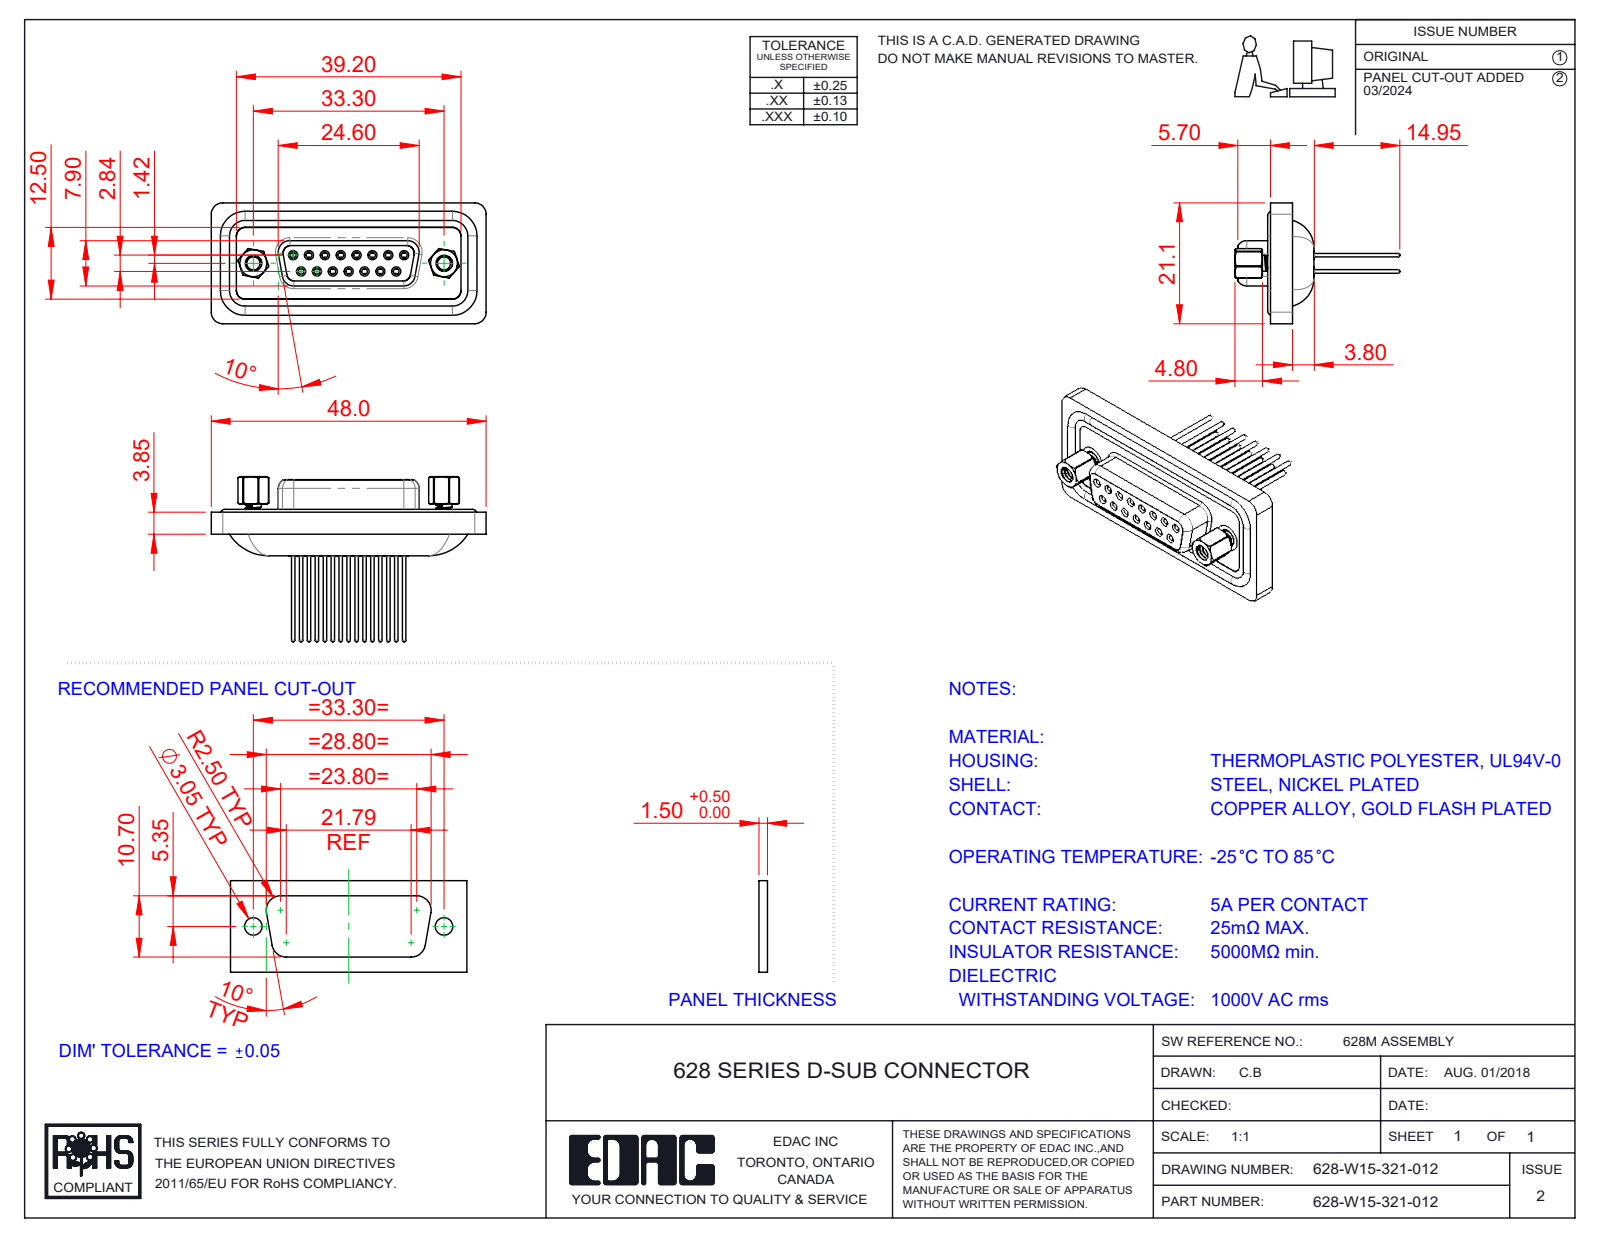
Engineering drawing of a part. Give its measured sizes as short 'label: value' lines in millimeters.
name: 628W Housing_15 Contacts; 628W Shell Front_15 Contacts; 628W 4-40 Threaded Rivet; 628-W15-321-012 (+4 more)
written by: SolidWorks 2020 (CONFIG_CONTROL_DESIGN)
unit: mm
bodies: 23 solids, 1278 faces (326 planar, 535 cylindrical, 417 other)
size: 48 × 28.3 × 21.1
volume: 6 416 mm³; area: 9 985 mm²
holes: 15× ⌀1, 15× ⌀1.1, 15× ⌀1.5, 15× ⌀1.7, 15× ⌀1.8, 15× ⌀2, 2× ⌀2.26, 2× ⌀2.29, 2× ⌀4, 2× ⌀4.8, 2× ⌀5
bosses: 19× ⌀1.6, 15× ⌀2.2, 15× ⌀0.6, 7× ⌀1.5, 2× ⌀4.9, 2× ⌀2.79
rounds: 16× R2, 14× R1.5, 8× R1.35, 6× R2.7, 4× R0.5, 4× R0.9, 4× R1.6, 4× R1.75
face distances: 0.4, 1.1, 2.75, 0.5, 3.75, 7.45, 7.5, 1, 13.65, 8.45
hole spacings: 3.16, 2.77, 5.54, 8.31, 5.03, 5.04, 7.48, 7.49
